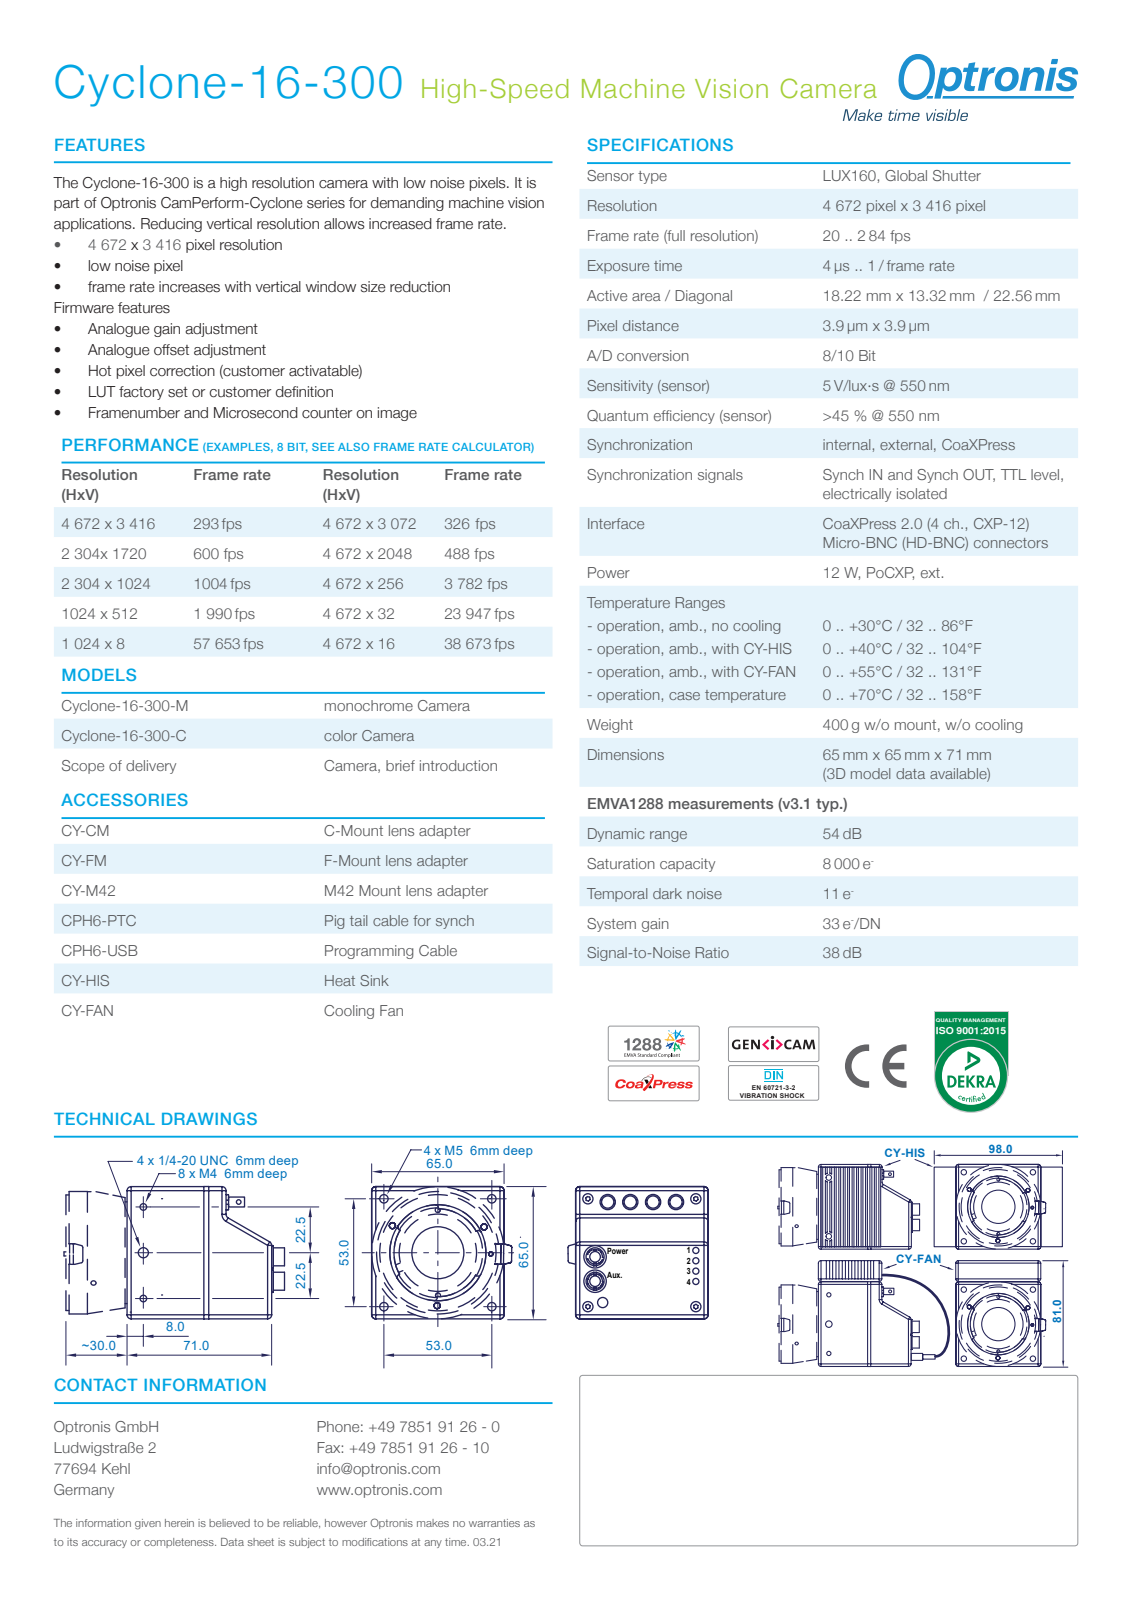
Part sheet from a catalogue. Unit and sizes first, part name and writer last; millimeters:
Units: millimetres
Overall size (bounding box): 77.3 × 65.02 × 65
Round holes (diameter × count): ⌀0.8 ×18, ⌀0.5 ×10, ⌀1.57 ×8, ⌀0.45 ×4, ⌀0.46 ×4, ⌀2.7 ×4, ⌀2.8 ×4, ⌀3.05 ×4, ⌀3.24 ×4, ⌀3.59 ×4, ⌀3.6 ×4, ⌀4 ×4
Round bosses / shafts (diameter × count): ⌀0.86 ×345, ⌀0.3 ×345, ⌀1.1 ×10, ⌀7.5 ×4, ⌀6.32 ×4, ⌀5.2 ×4, ⌀4.55 ×4, ⌀4.5 ×4
Partial cylindrical surfaces — rounded edges, fillets, slot ends (radius × count): R3 ×32, R1 ×28, R2 ×22, R0.5 ×12, R0.2 ×10, R0.45 ×10, R0.16 ×8, R2.1 ×4
Main face-to-face distances: 2, 63, 65, 61, 59, 4.8, 3, 58.5, 0.5, 27.9
Hole centre spacings: 1.8, 3.12, 53, 1.6, 2.26, 11.2, 22.5, 37.48
Volume: 88 157 mm³ · Surface area: 69 713 mm²
Bodies: 7 solids, 3972 faces (2000 planar, 1456 cylindrical, 516 other)
Part name (STEP PRODUCT): 1200-MG-01-D_Cyclone
STEP written by: Autodesk Inventor 2026 (AUTOMOTIVE_DESIGN)
